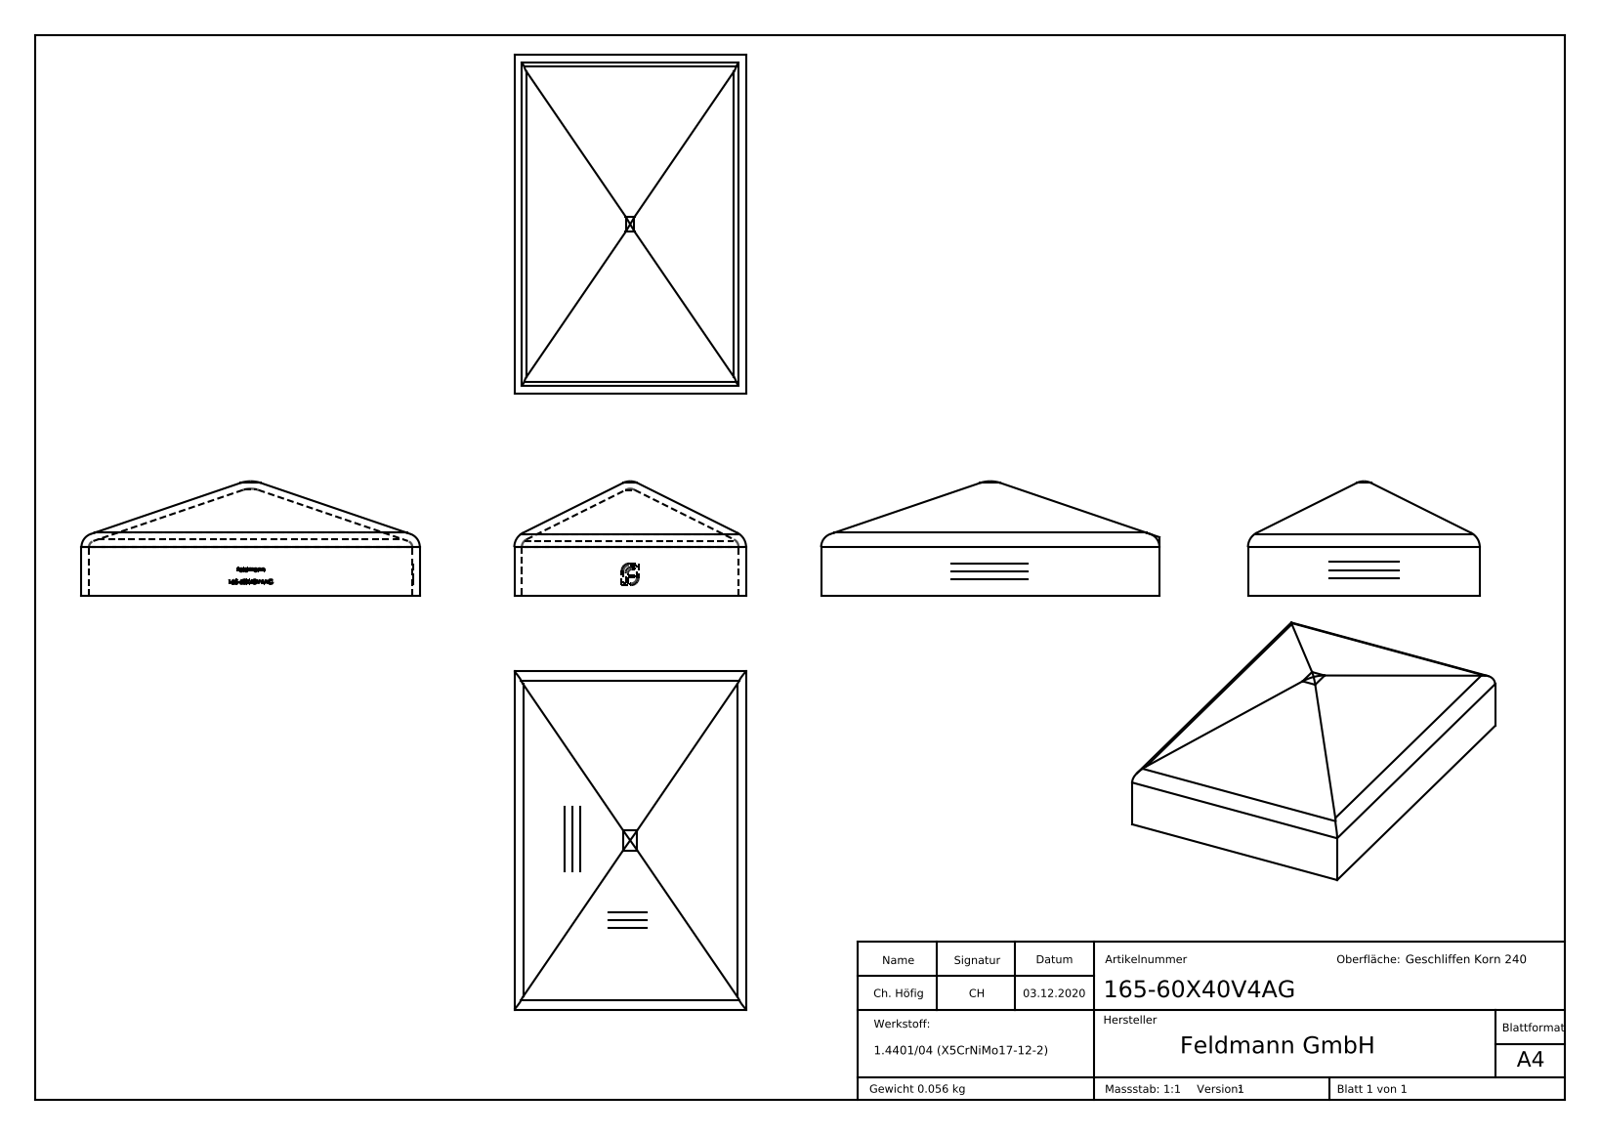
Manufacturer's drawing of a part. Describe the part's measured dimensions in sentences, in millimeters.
The part is named "165-60X40V4AG". Its 3-D file was written by "SolidWorks 2018 (CONFIG_CONTROL_DESIGN)". It is 1 solid with 342 faces: 205 planar, 16 cylindrical and 121 other. Overall it measures 63.5 by 43.5 by 21.5 millimeters. Its volume is 6 958 cubic millimeters and its surface area 10 249 square millimeters. Partial cylindrical surfaces (rounded edges, fillets, slot ends): 3 of radius 1.6, 3 of radius 3, 2 of radius 1.19, 2 of radius 2.59, 1 of radius 4.49, 1 of radius 5.89. The main face-to-face distances are 1.4, 42.1, 62.1, 43.5, 40.7, 63.5, 60.7, 1.3, 60.8, 62.2.
